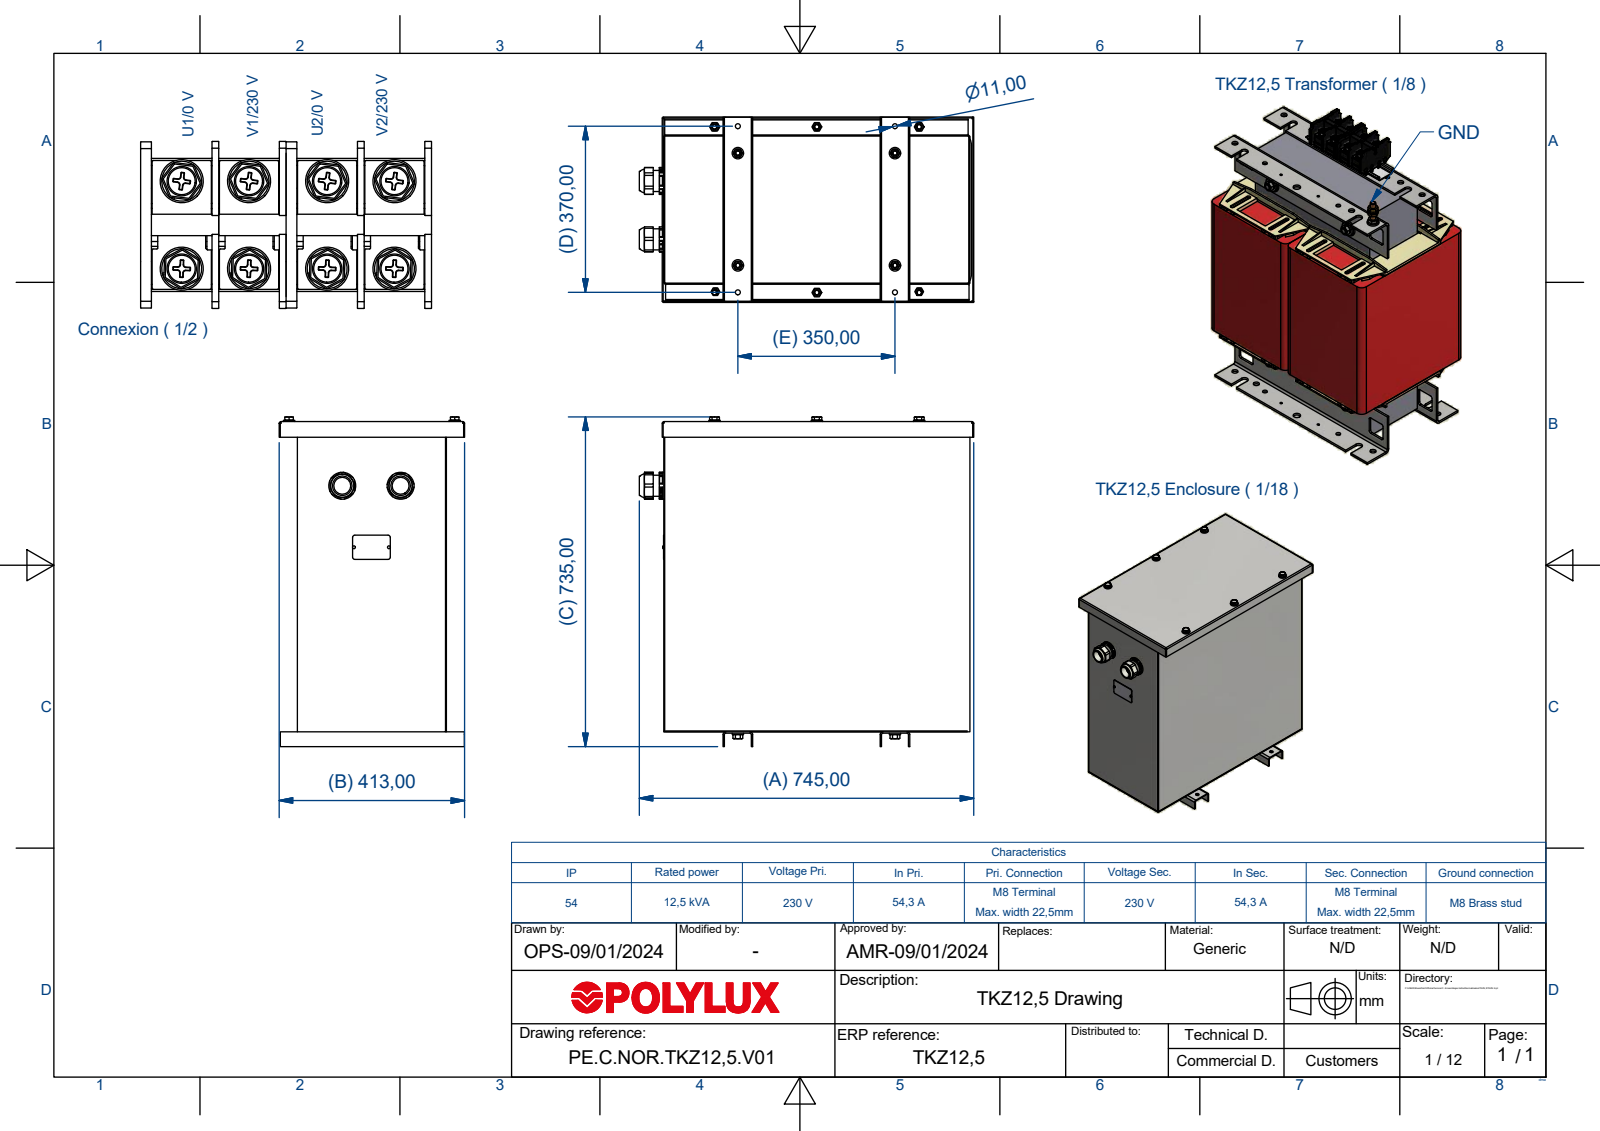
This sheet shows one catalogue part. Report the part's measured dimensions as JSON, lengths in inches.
{"part_name": "TKZ12,5", "step_written_by": "Autodesk Inventor 2018 (AUTOMOTIVE_DESIGN)", "units": "inches", "bodies": {"solids": 43, "faces": 993, "planar": 558, "cylindrical": 177, "other": 258}, "overall_size": [29.331, 28.909, 16.26], "volume_in3": 292.7, "surface_area_in2": 7031, "round_holes": [[0.472, 10], [0.524, 10], [0.398, 8], [0.433, 8], [0.441, 4], [0.33, 3], [0.138, 2], [0.157, 2], [1.476, 2], [1.673, 2], [1.89, 2]], "round_bosses_or_shafts": [[1, 10], [0.677, 10], [0.435, 10], [0.472, 4], [2.362, 2], [1.85, 2], [1.713, 2], [0.252, 2]], "partial_cylinders_radius": [[0.157, 16], [0.079, 12], [0.118, 4], [0.197, 4], [0.236, 4], [0.591, 4], [1.378, 4]], "face_to_face_distances": [0.079, 12.992, 27.126, 26.772, 12.913, 13.071, 26.85, 27.205, 27.047, 26.693], "hole_center_spacings": [14.528, 13.78, 0.039, 17.874, 17.913, 1.142, 1.22, 2.362]}
